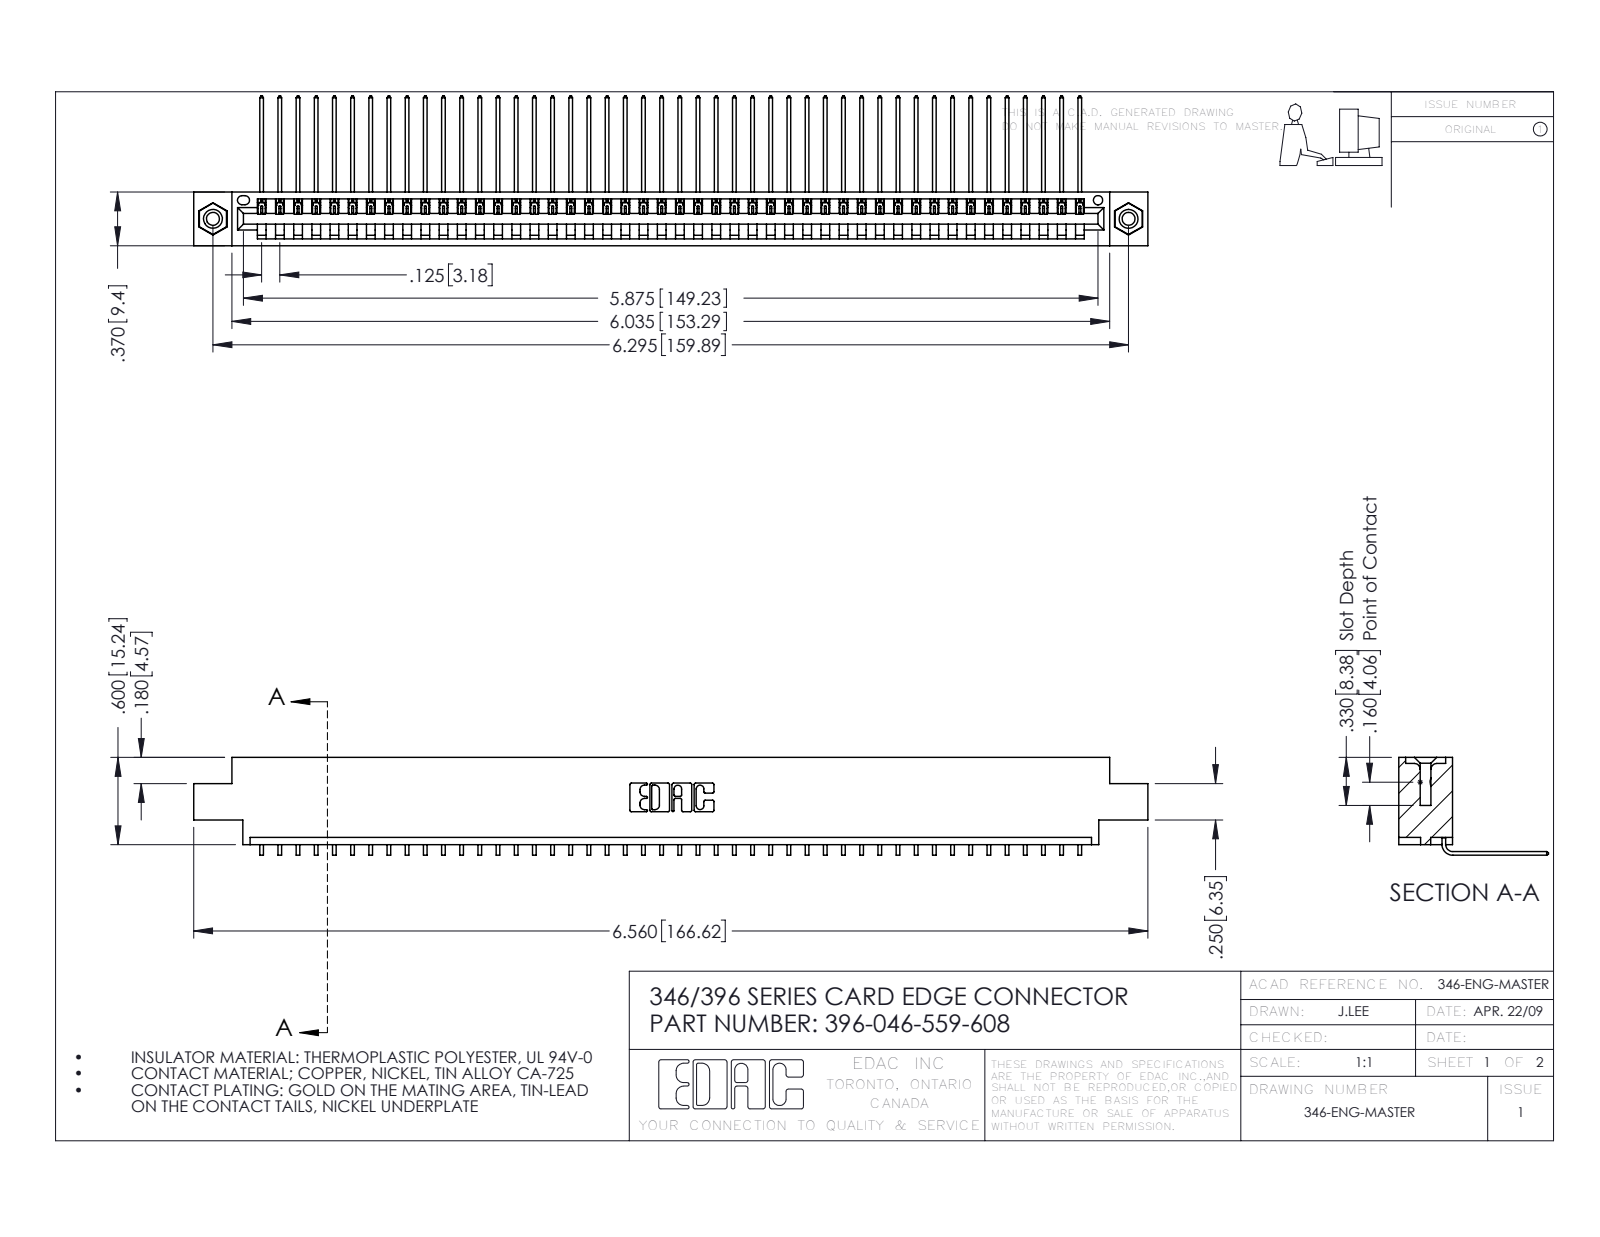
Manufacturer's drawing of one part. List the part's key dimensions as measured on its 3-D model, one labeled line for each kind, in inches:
Part name (STEP PRODUCT): 346 Part_0.170 Offset - 0.156 Dia-TI; 345-292-001_558 559 Tail - 1; 345-250-001_345-250-003-102; 396-046-559-608
STEP written by: SolidWorks 2016 (CONFIG_CONTROL_DESIGN)
Units: inches
Bodies: 49 solids, 2946 faces (2044 planar, 886 cylindrical, 16 other)
Overall size (bounding box): 6.56 × 1.03 × 0.673
Volume: 0.975 in³ · Surface area: 32.7 in²
Round holes (diameter × count): ⌀0.089 ×2, ⌀0.125 ×2, ⌀0.156 ×2, ⌀0.064 ×1
Round bosses / shafts (diameter × count): ⌀0.155 ×2
Partial cylindrical surfaces — rounded edges, fillets, slot ends (radius × count): R0.006 ×92, R0.01 ×22, R0.007 ×6, R0.031 ×6, R0.026 ×3, R0.031 ×2, R0.04 ×2, R0.014 ×1
Main face-to-face distances: 0.048, 0.322, 0.37, 0.025, 0.25, 0.072, 0.222, 0.298, 0.148, 0.1
Hole centre spacings: 0.246, 6.086, 6.295
